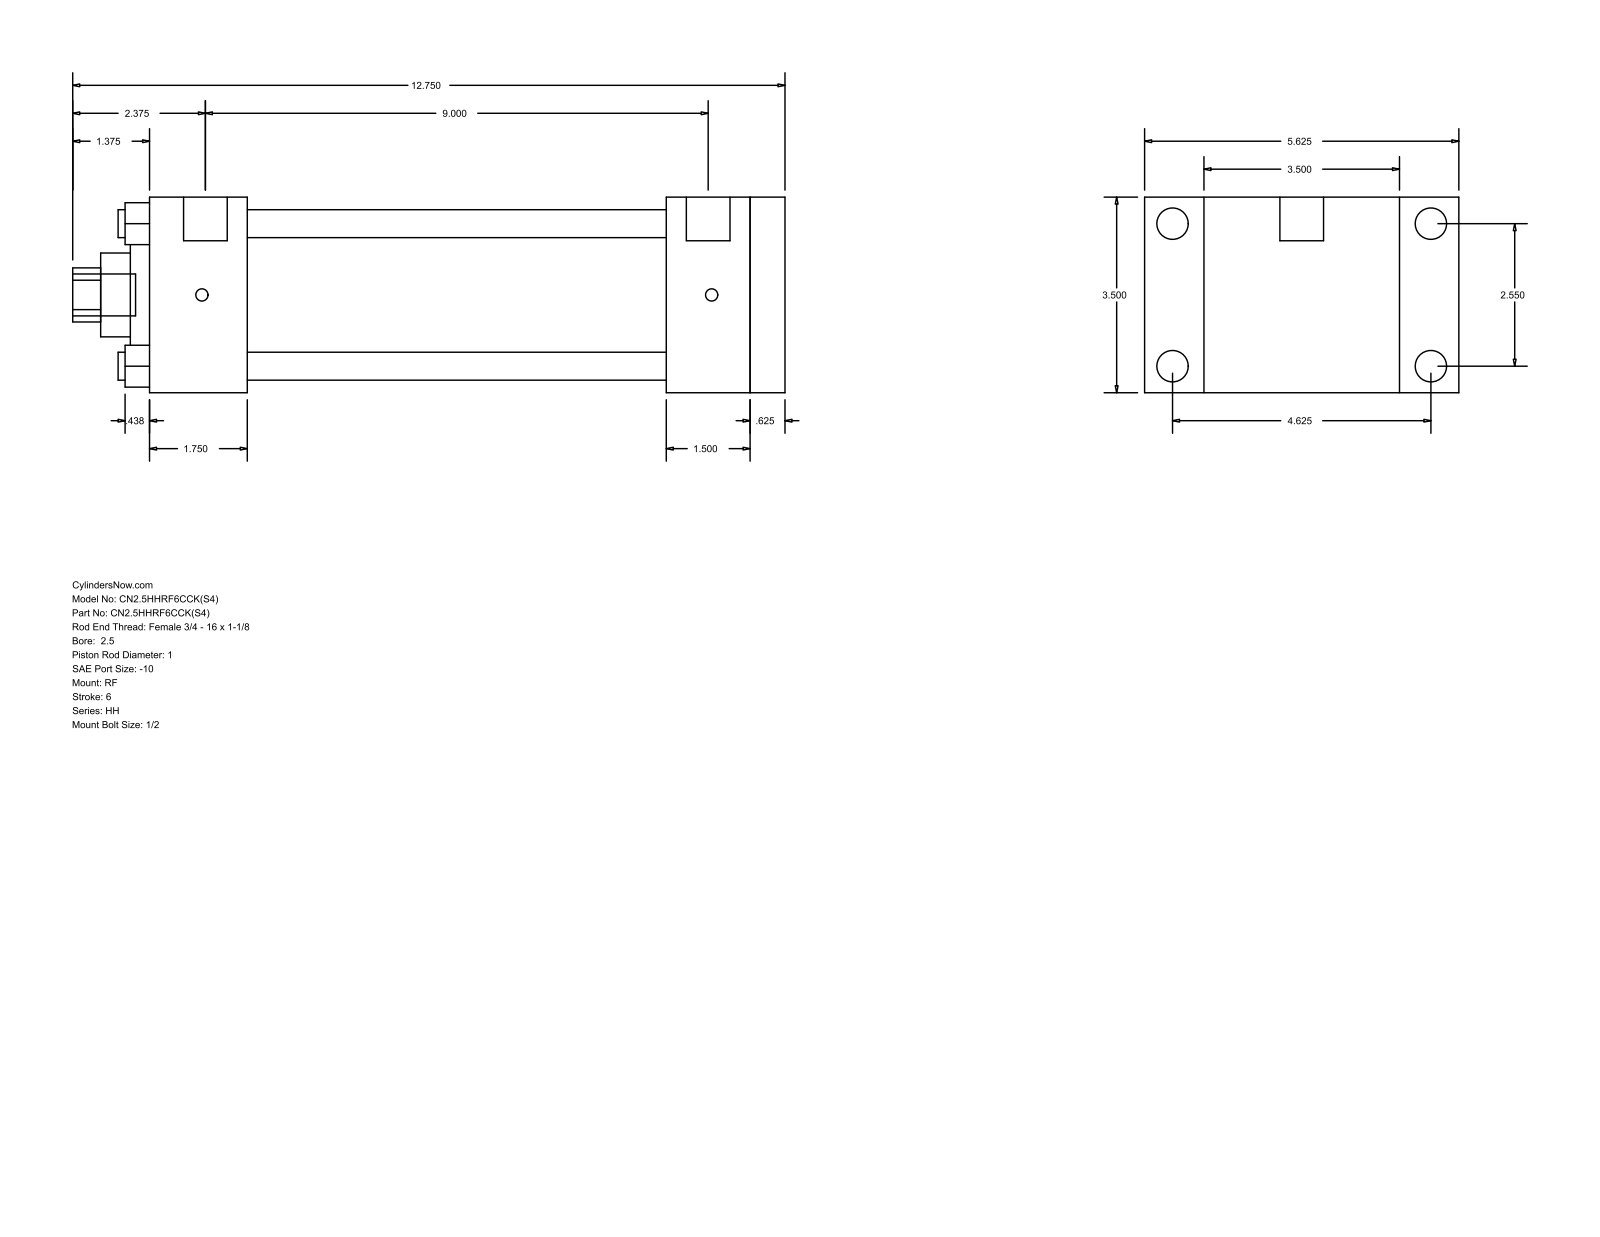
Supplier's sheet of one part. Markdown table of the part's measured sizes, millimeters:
| quantity | value |
| --- | --- |
| part name | HH_RF__0250_1 |
| STEP written by | GSSL Pune (CONFIG_CONTROL_DESIGN) |
| units | millimeters |
| bodies | 0 solids, 94 faces (65 planar, 29 cylindrical, 0 other) |
| overall size | 323.85 × 142.88 × 88.9 |
| round holes (diameter × count) | 12.7 × 4, 25.4 × 1, 38.1 × 1, 60.33 × 1, 73.03 × 1 |
| round bosses / shafts (diameter × count) | 14.3 × 4, 5.56 × 4, 19.84 × 2, 19.05 × 1 |
| partial cylindrical surfaces (radius × count) | 12.29 × 1 |
| main face-to-face distances | 88.9, 15.87, 273.06, 288.93, 44.46, 228.6, 244.47, 234.96, 190.5, 38.1 |
| hole center spacings | 45.79, 64.76, 91.58 |
